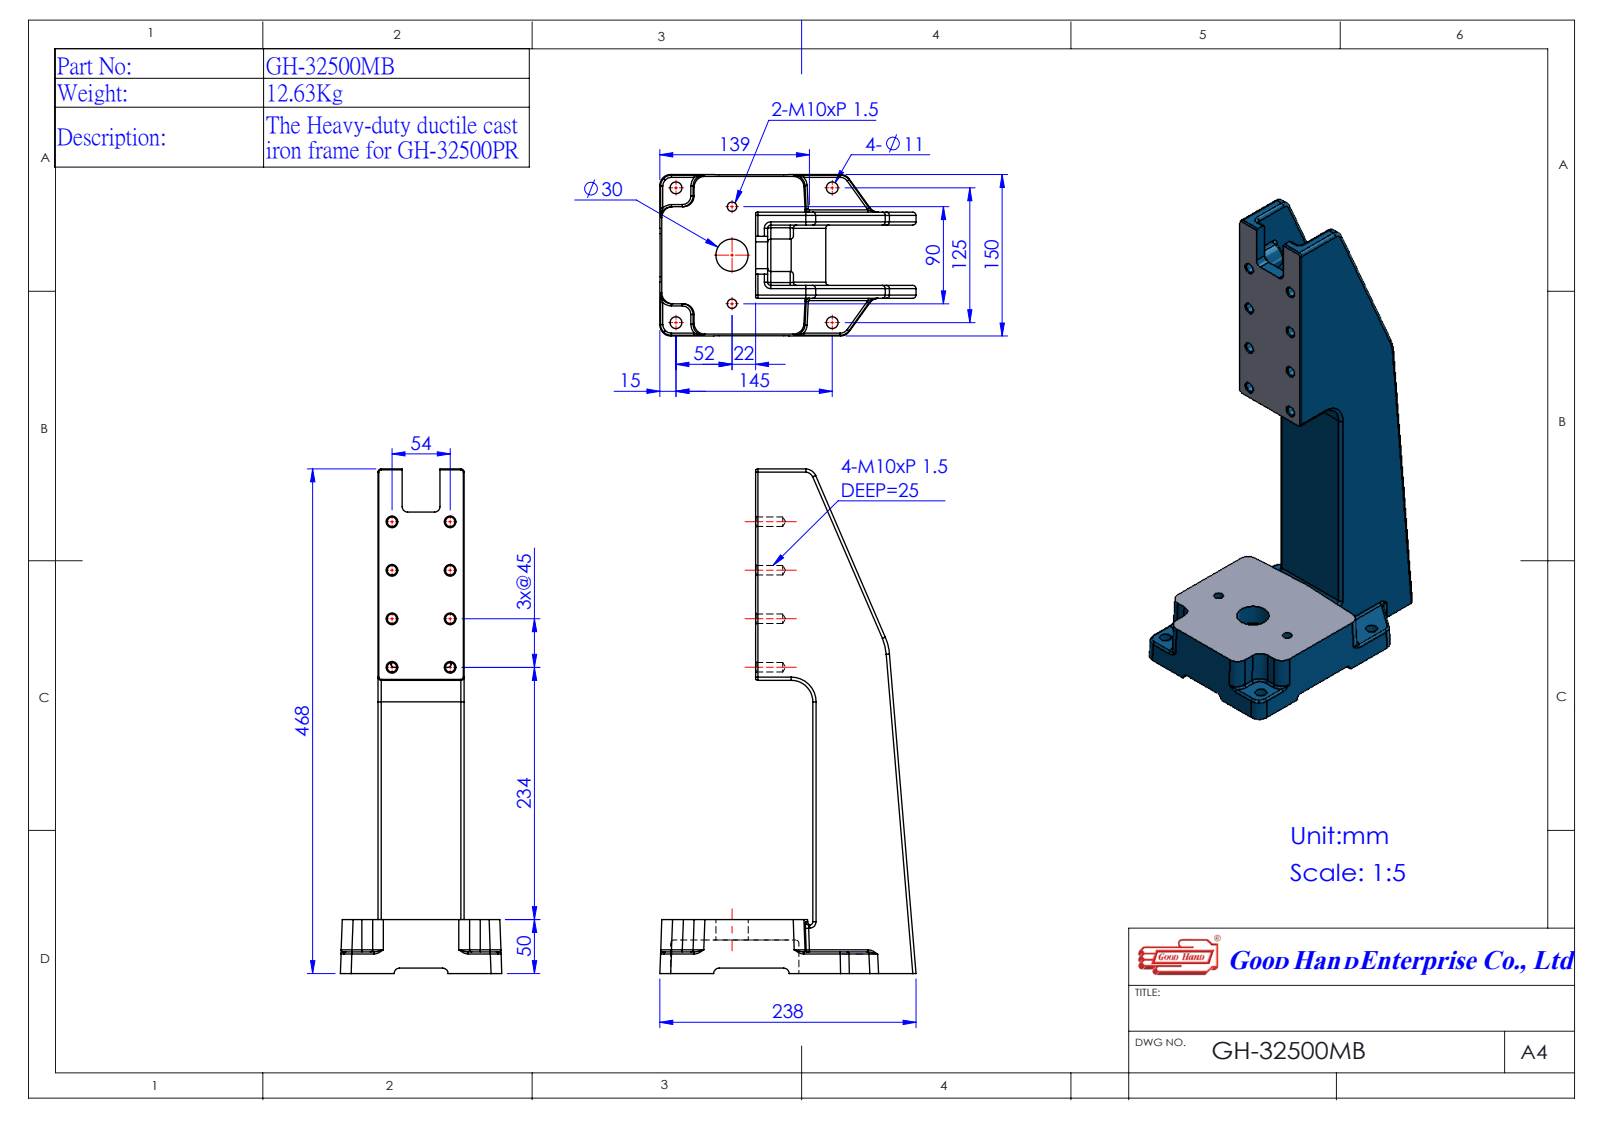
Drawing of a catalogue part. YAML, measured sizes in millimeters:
part_name: "GH-32500MB(簡化)-1^GH-32500PR(簡化)-1"
step_written_by: "SolidWorks 2016 (AUTOMOTIVE_DESIGN)"
units: millimeters
bodies: {solids: 1, faces: 283, planar: 60, cylindrical: 135, other: 88}
overall_size: [468, 237.65, 149.79]
volume: 1870000
surface_area: 320831
round_holes:
  - {diameter: 8.5, count: 10}
  - {diameter: 11, count: 4}
  - {diameter: 30, count: 1}
partial_cylinders:
  - {radius: 3, count: 45}
  - {radius: 10, count: 23}
  - {radius: 12, count: 8}
  - {radius: 5, count: 4}
  - {radius: 20, count: 3}
  - {radius: 32, count: 1}
  - {radius: 50, count: 1}
face_to_face_distances: [12, 68, 80, 56, 19, 53, 65, 11, 31, 50]
hole_center_spacings: [45, 70.29, 90, 54, 104.96, 54.87, 81.3, 94.63]
